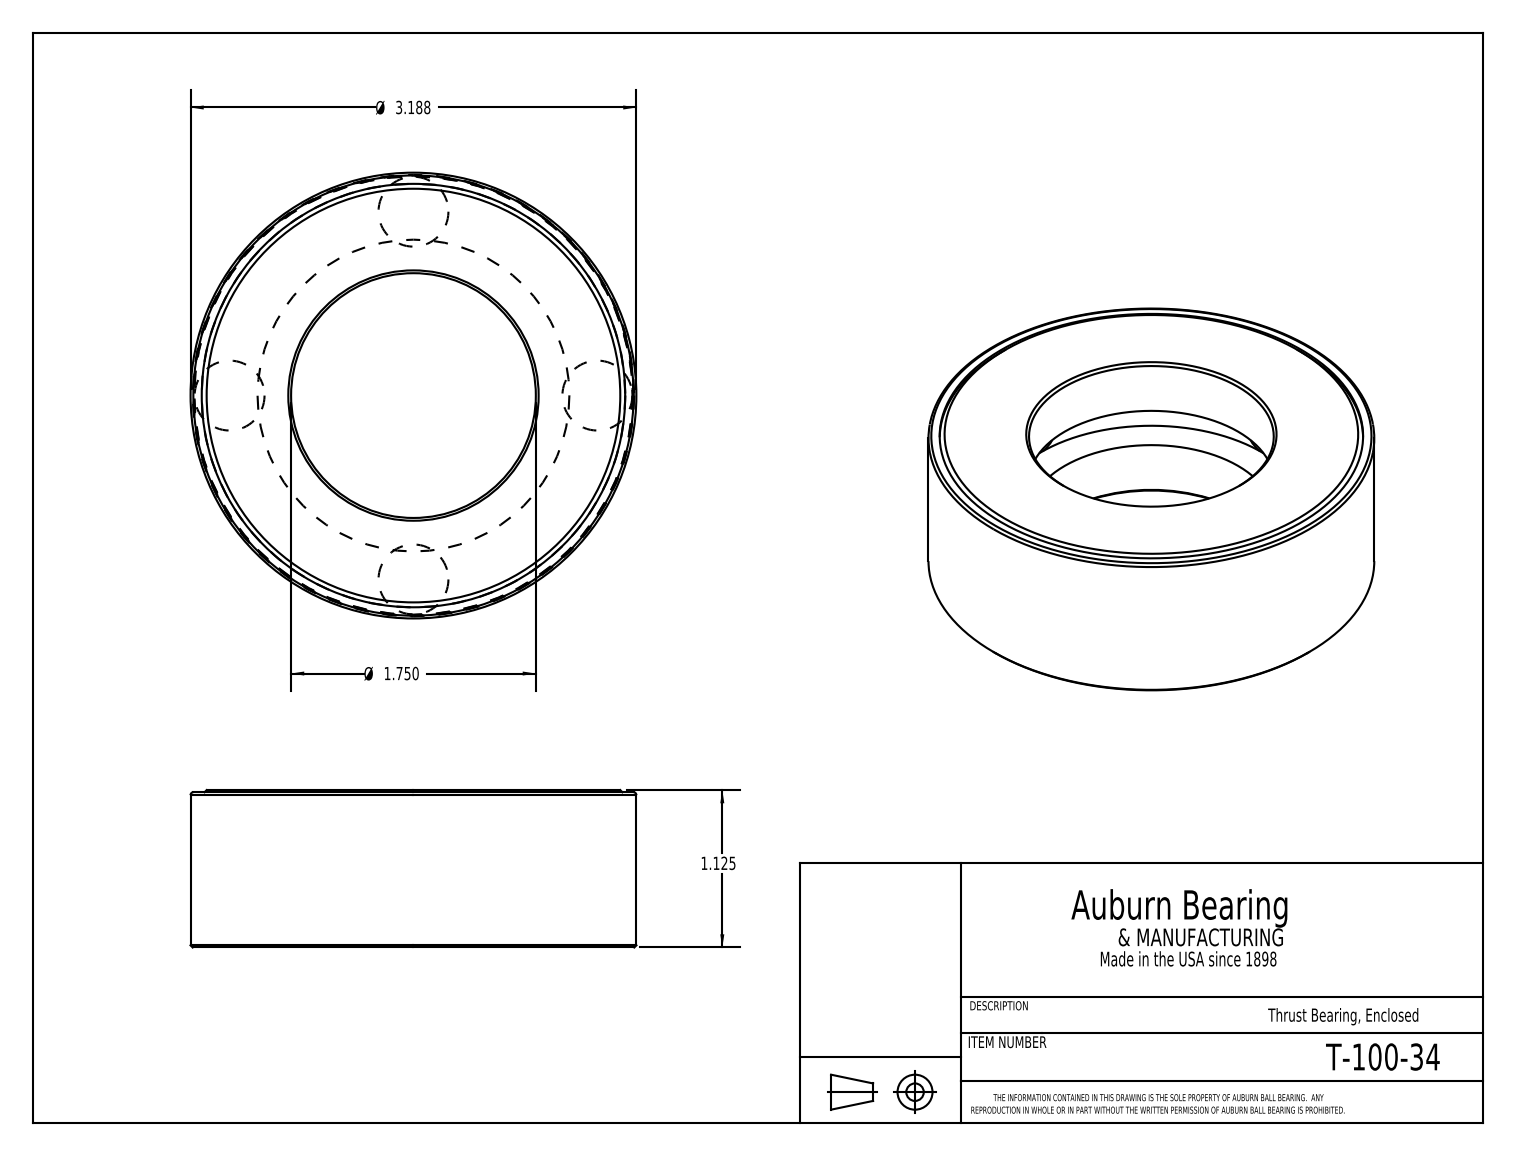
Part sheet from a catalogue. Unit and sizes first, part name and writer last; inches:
Units: inches
Overall size (bounding box): 3.188 × 3.188 × 1.125
Round holes (diameter × count): ⌀1.75 ×1, ⌀3.027 ×1, ⌀3.147 ×1
Round bosses / shafts (diameter × count): ⌀3.187 ×1, ⌀3.133 ×1
Main face-to-face distances: 1.125, 0.413, 0.712, 0.713, 0.3, 0.412, 1.09, 0.678, 0.378, 0.035
Volume: 4.397 in³ · Surface area: 52.97 in²
Bodies: 6 solids, 28 faces (9 planar, 7 cylindrical, 12 other)
Part name (STEP PRODUCT): T-100-34
STEP written by: SolidWorks 2016 (CONFIG_CONTROL_DESIGN)
